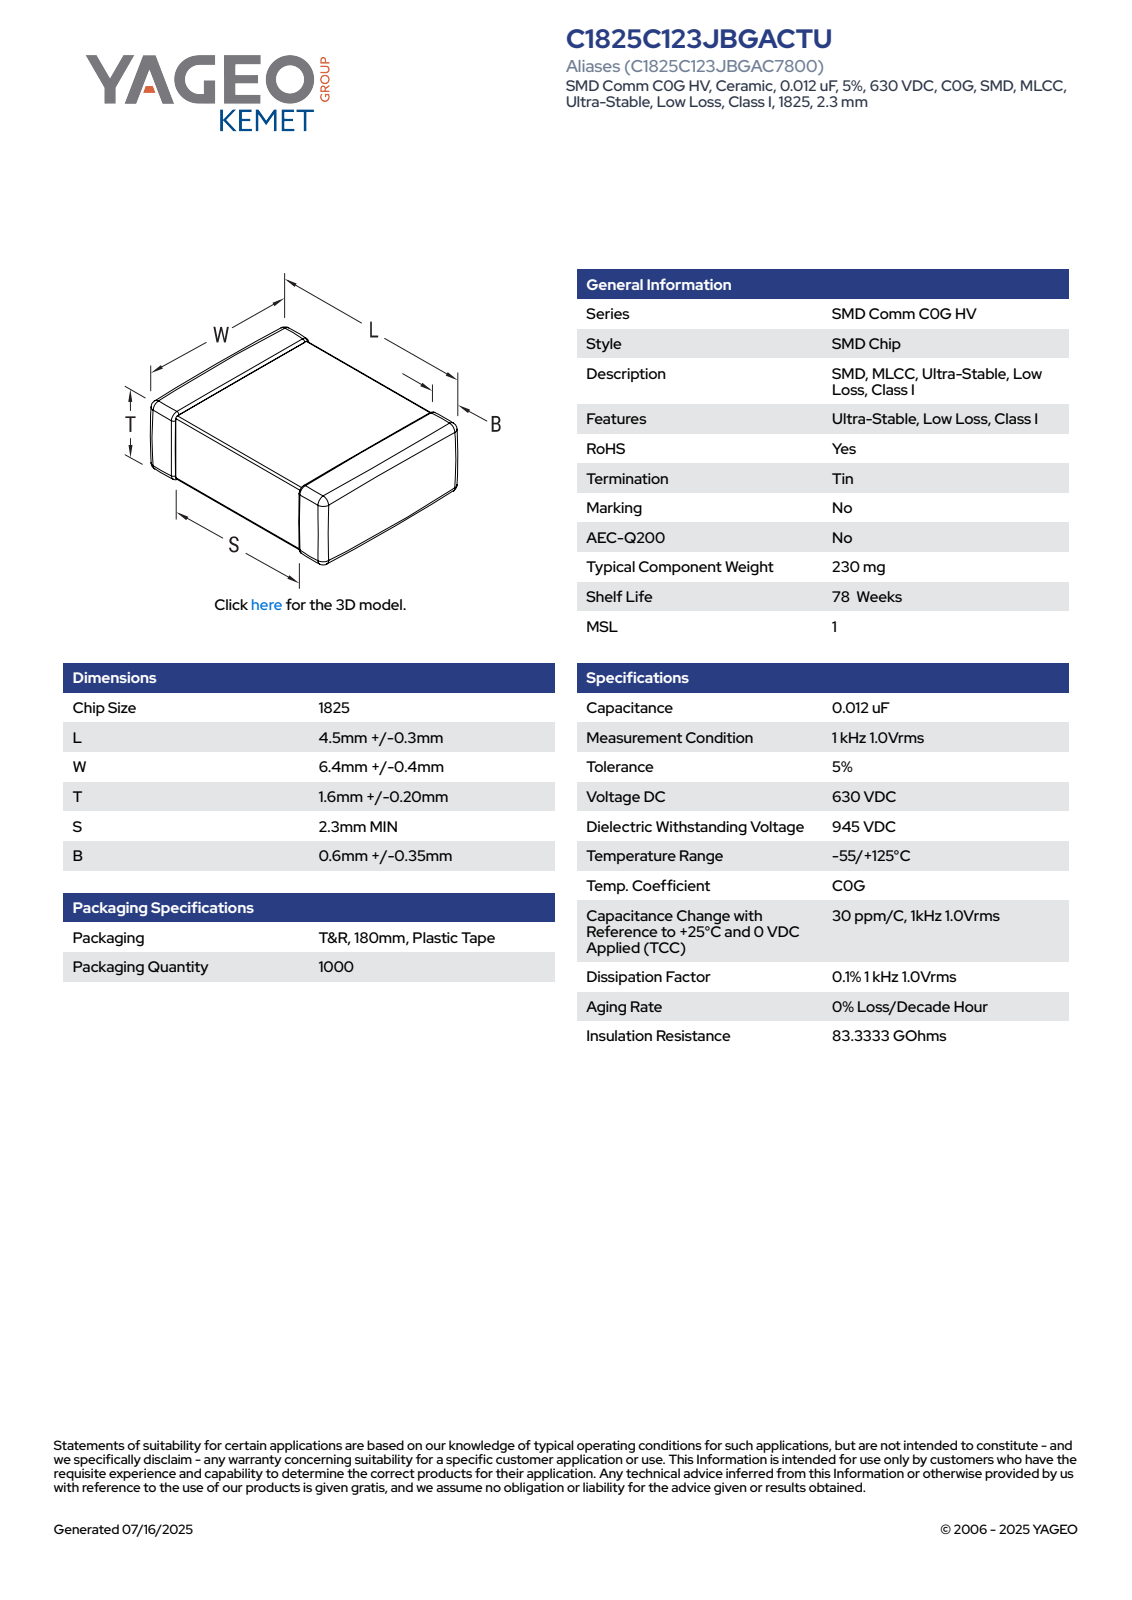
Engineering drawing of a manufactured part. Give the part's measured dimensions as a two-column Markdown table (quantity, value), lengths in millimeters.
| quantity | value |
| --- | --- |
| part name | CCS_CCSTDNOS_1825_L4.8W6.8T1.8B0.95 |
| STEP written by | SolidWorks 2014 (AUTOMOTIVE_DESIGN) |
| units | millimeters |
| bodies | 4 solids, 125 faces (71 planar, 38 cylindrical, 16 other) |
| overall size | 6.8 × 4.8 × 1.8 |
| volume | 52 mm³ |
| surface area | 104 mm² |
| partial cylindrical surfaces (radius × count) | 0.14 × 24 |
| main face-to-face distances | 1.52, 1.66, 4.8, 1.8, 6.66, 6.52, 6.8, 0.34, 3.56, 3.42 |
